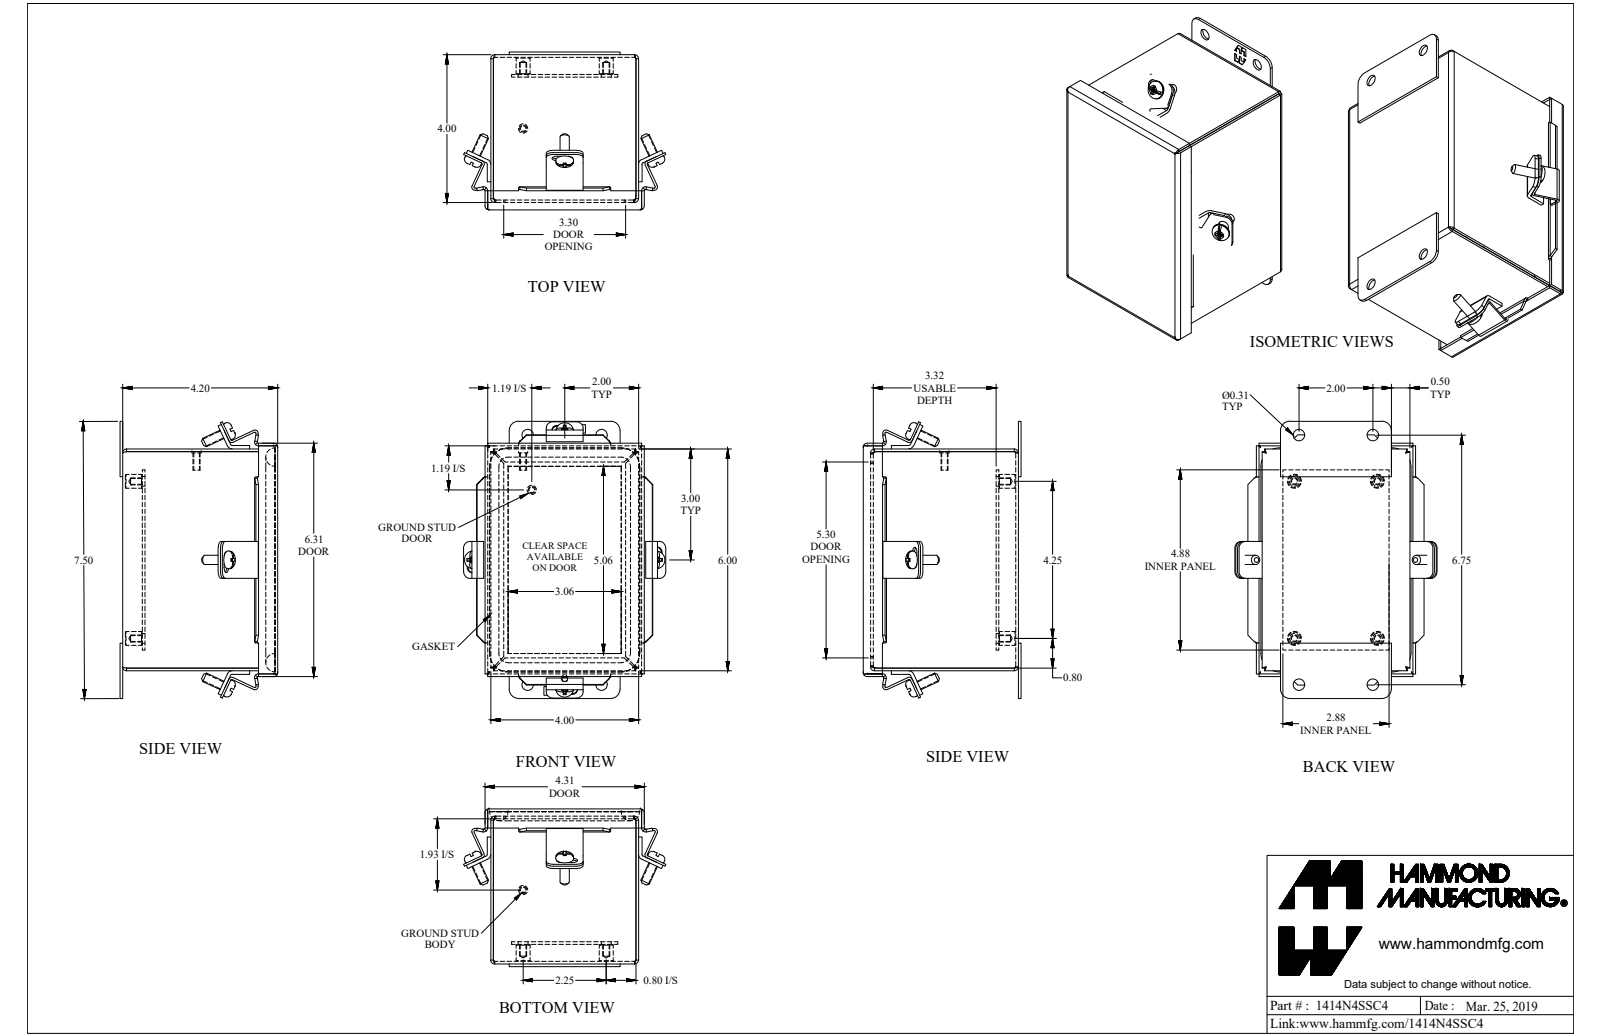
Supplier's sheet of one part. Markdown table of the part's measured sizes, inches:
| quantity | value |
| --- | --- |
| part name | 1414N4SSC4 |
| STEP written by | SolidWorks 2018 (AUTOMOTIVE_DESIGN) |
| units | inches |
| bodies | 24 solids, 655 faces (411 planar, 168 cylindrical, 76 other) |
| overall size | 7.5 × 5.475 × 4.269 |
| volume | 14.93 in³ |
| surface area | 415.5 in² |
| round holes (diameter × count) | 0.156 × 4, 0.213 × 4, 0.265 × 4, 0.313 × 4 |
| round bosses / shafts (diameter × count) | 0.25 × 6, 0.48 × 4, 0.375 × 4, 0.19 × 2 |
| partial cylindrical surfaces (radius × count) | 0.25 × 20, 0.188 × 16, 0.036 × 12, 0.108 × 12, 0.01 × 8, 0.029 × 8, 0.086 × 8, 0.141 × 8 |
| main face-to-face distances | 0.072, 3.928, 4.125, 4.197, 4, 5.928, 3.593, 0.532, 3.856, 0.604 |
| hole center spacings | 2.25, 1.257, 4.809, 5.502, 2.465, 2.466, 5.896, 1.256 |
